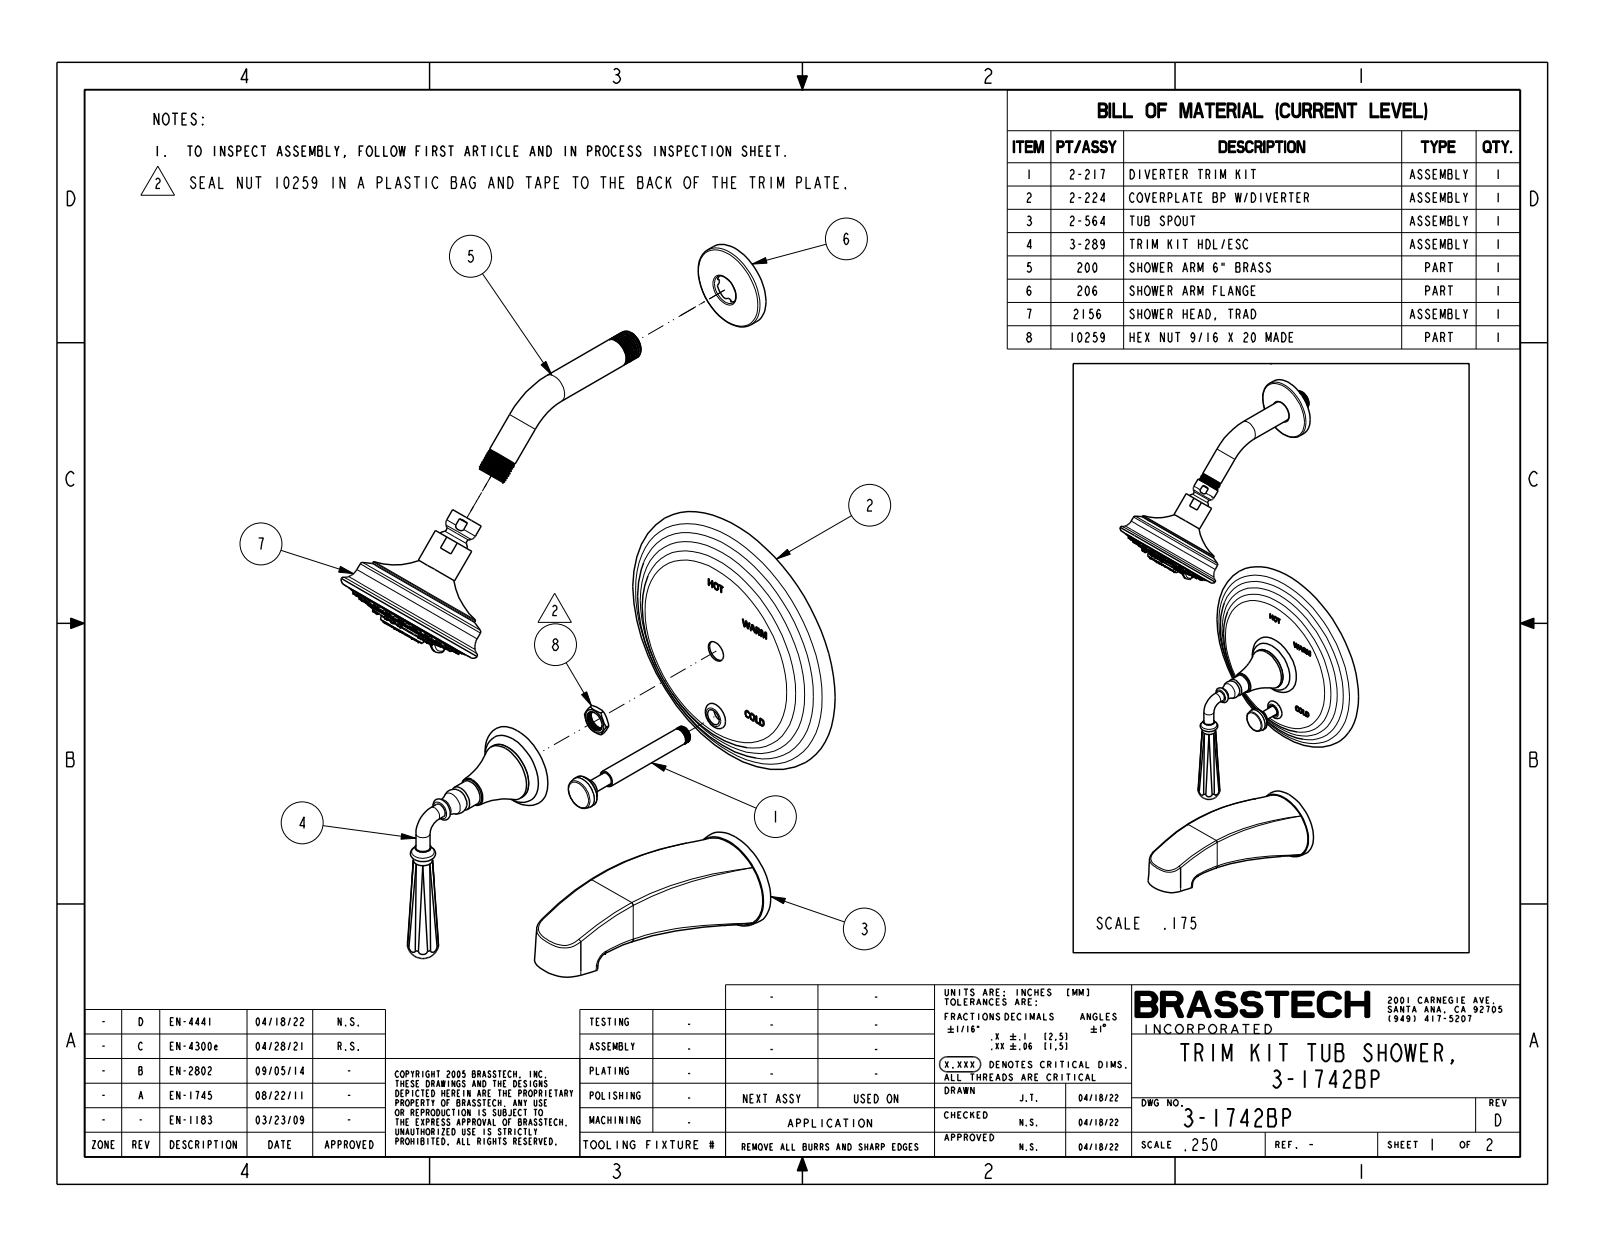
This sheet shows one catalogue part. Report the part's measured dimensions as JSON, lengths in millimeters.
{"part_name": "3-1742BP", "step_written_by": "CREO PARAMETRIC BY PTC INC, 2018400 (CONFIG_CONTROL_DESIGN)", "units": "millimeters", "bodies": {"solids": 3, "faces": 1348, "planar": 250, "cylindrical": 212, "other": 886}, "overall_size": [572.9, 209.6, 196.9], "volume_mm3": 1229000, "surface_area_mm2": 163200, "round_holes": [[1.5, 8], [23.5, 1]], "round_bosses_or_shafts": [[3.6, 39], [4.2, 23], [20.7, 2], [9.9, 2], [96.8, 1], [94.6, 1], [82.3, 1], [60.5, 1]], "partial_cylinders_radius": [[2, 8], [0.5, 2], [3.5, 1], [12, 1], [13, 1], [16, 1]], "face_to_face_distances": [19.2, 1.6, 3, 4.6, 29.6, 48.8, 45.1, 64.2, 15.4, 73.2], "hole_center_spacings": [11.3, 14.7, 20.8, 20.8, 27.2, 11.3, 14.7, 27.2]}
